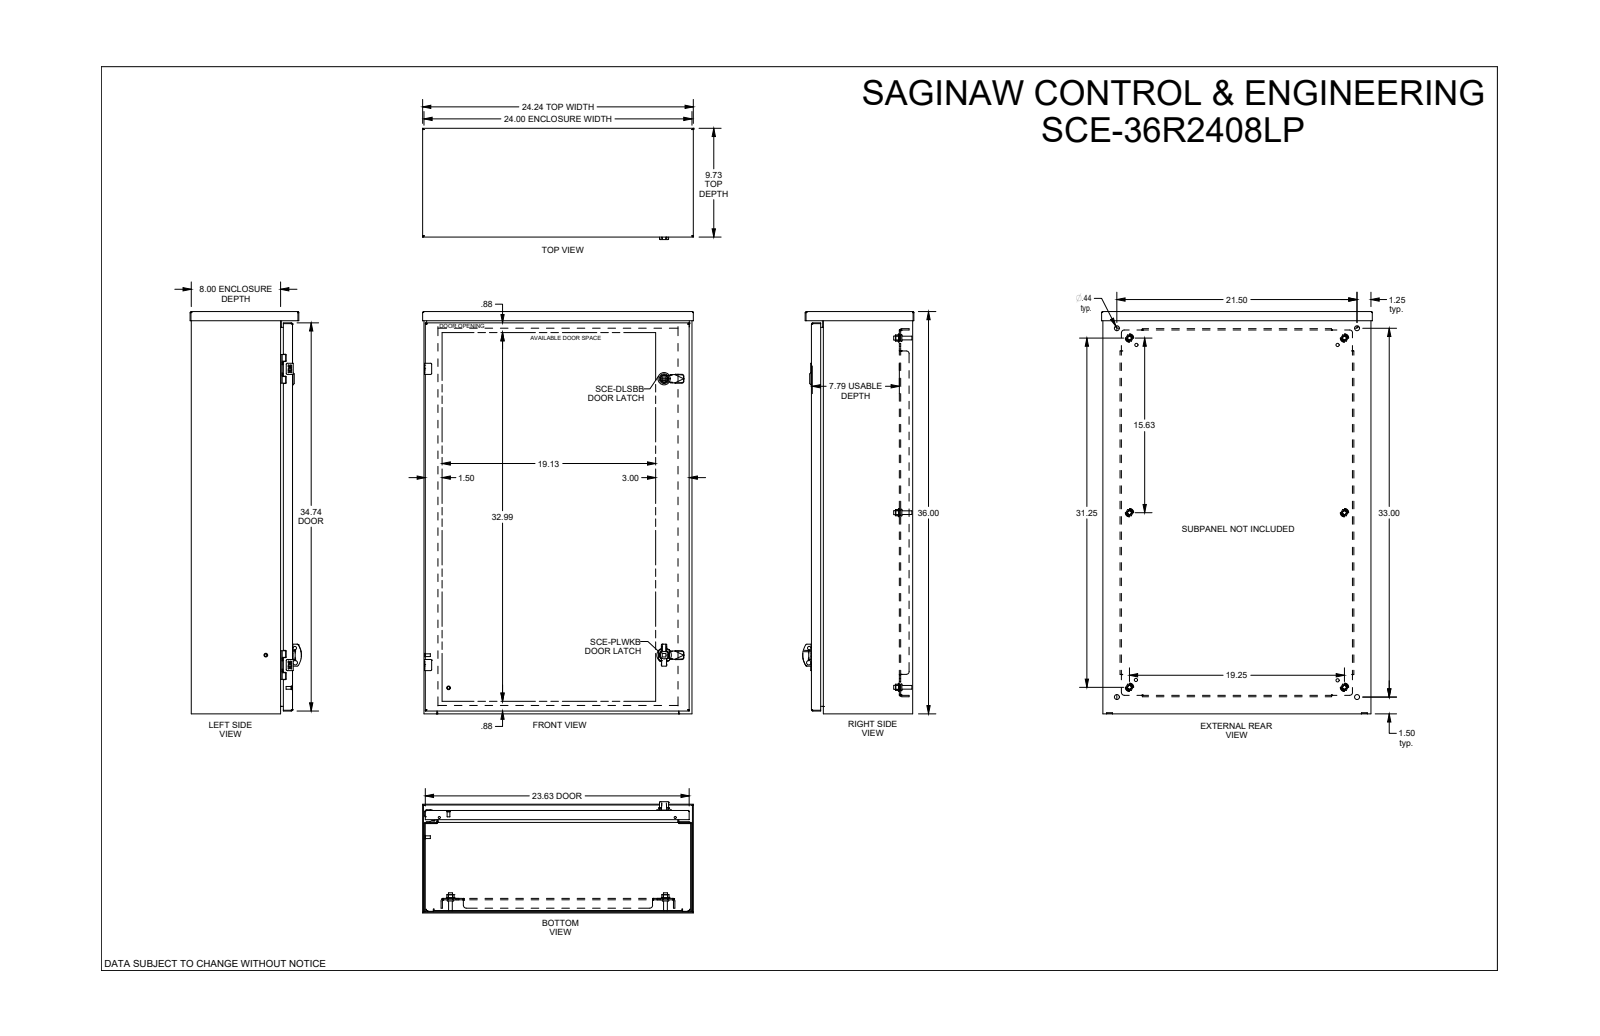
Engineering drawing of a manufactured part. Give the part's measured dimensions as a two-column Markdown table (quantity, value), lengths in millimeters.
| quantity | value |
| --- | --- |
| part name | SCE-36R2408LP |
| STEP written by | SolidWorks 2019 (CONFIG_CONTROL_DESIGN) |
| units | millimeters |
| bodies | 0 solids, 2607 faces (1214 planar, 875 cylindrical, 518 other) |
| overall size | 914.4 × 615.6 × 252.9 |
| round holes (diameter × count) | 9.3 × 6, 12.7 × 6, 4.4 × 4, 5.2 × 4, 6.2 × 4, 6.8 × 4, 7.1 × 4, 9.5 × 4, 11.1 × 4, 1 × 2, 4 × 2, 4.8 × 2 |
| round bosses / shafts (diameter × count) | 9.3 × 6, 8.4 × 6, 4.3 × 6, 6.4 × 4, 6.1 × 4, 5 × 3, 22 × 2, 20.4 × 2 |
| partial cylindrical surfaces (radius × count) | 0.4 × 70, 0.3 × 60, 1.5 × 46, 0.3 × 38, 0.5 × 24, 3 × 19, 1.1 × 17, 0.8 × 15 |
| main face-to-face distances | 1.9, 1.9, 226.5, 228.4, 230.3, 228.4, 3.2, 25.4, 201.1, 30.5 |
| hole center spacings | 673.1, 12.5, 22.2, 36.2, 396.9, 420.1, 518, 629.7 |
